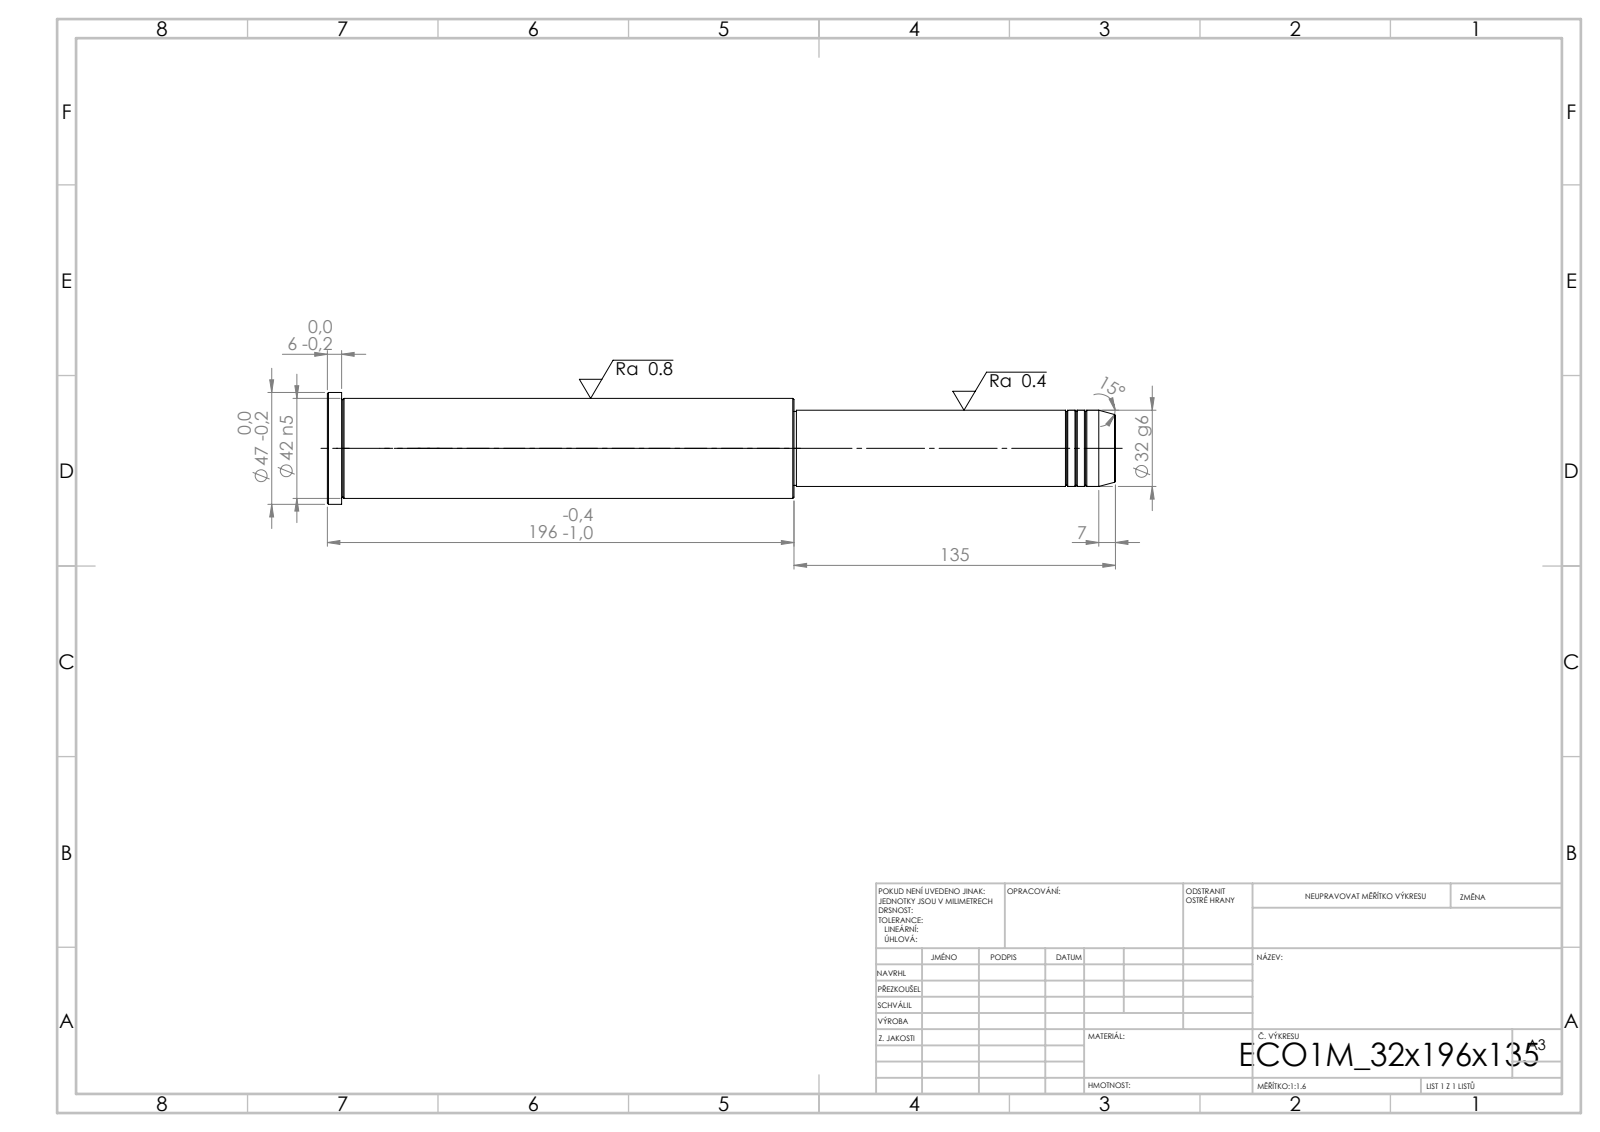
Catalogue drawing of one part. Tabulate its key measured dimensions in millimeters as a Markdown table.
| quantity | value |
| --- | --- |
| STEP written by | SolidWorks 2019 (CONFIG_CONTROL_DESIGN) |
| units | millimeters |
| bodies | 1 solid, 43 faces (5 planar, 14 cylindrical, 24 other) |
| overall size | 331 × 47 × 47 |
| volume | 381 328 mm³ |
| surface area | 43 040 mm² |
| round bosses / shafts (diameter × count) | 47 × 1, 42 × 1, 32 × 1, 31 × 1 |
| main face-to-face distances | 331, 135, 196, 325, 190, 6, 134, 1, 191, 197 |
